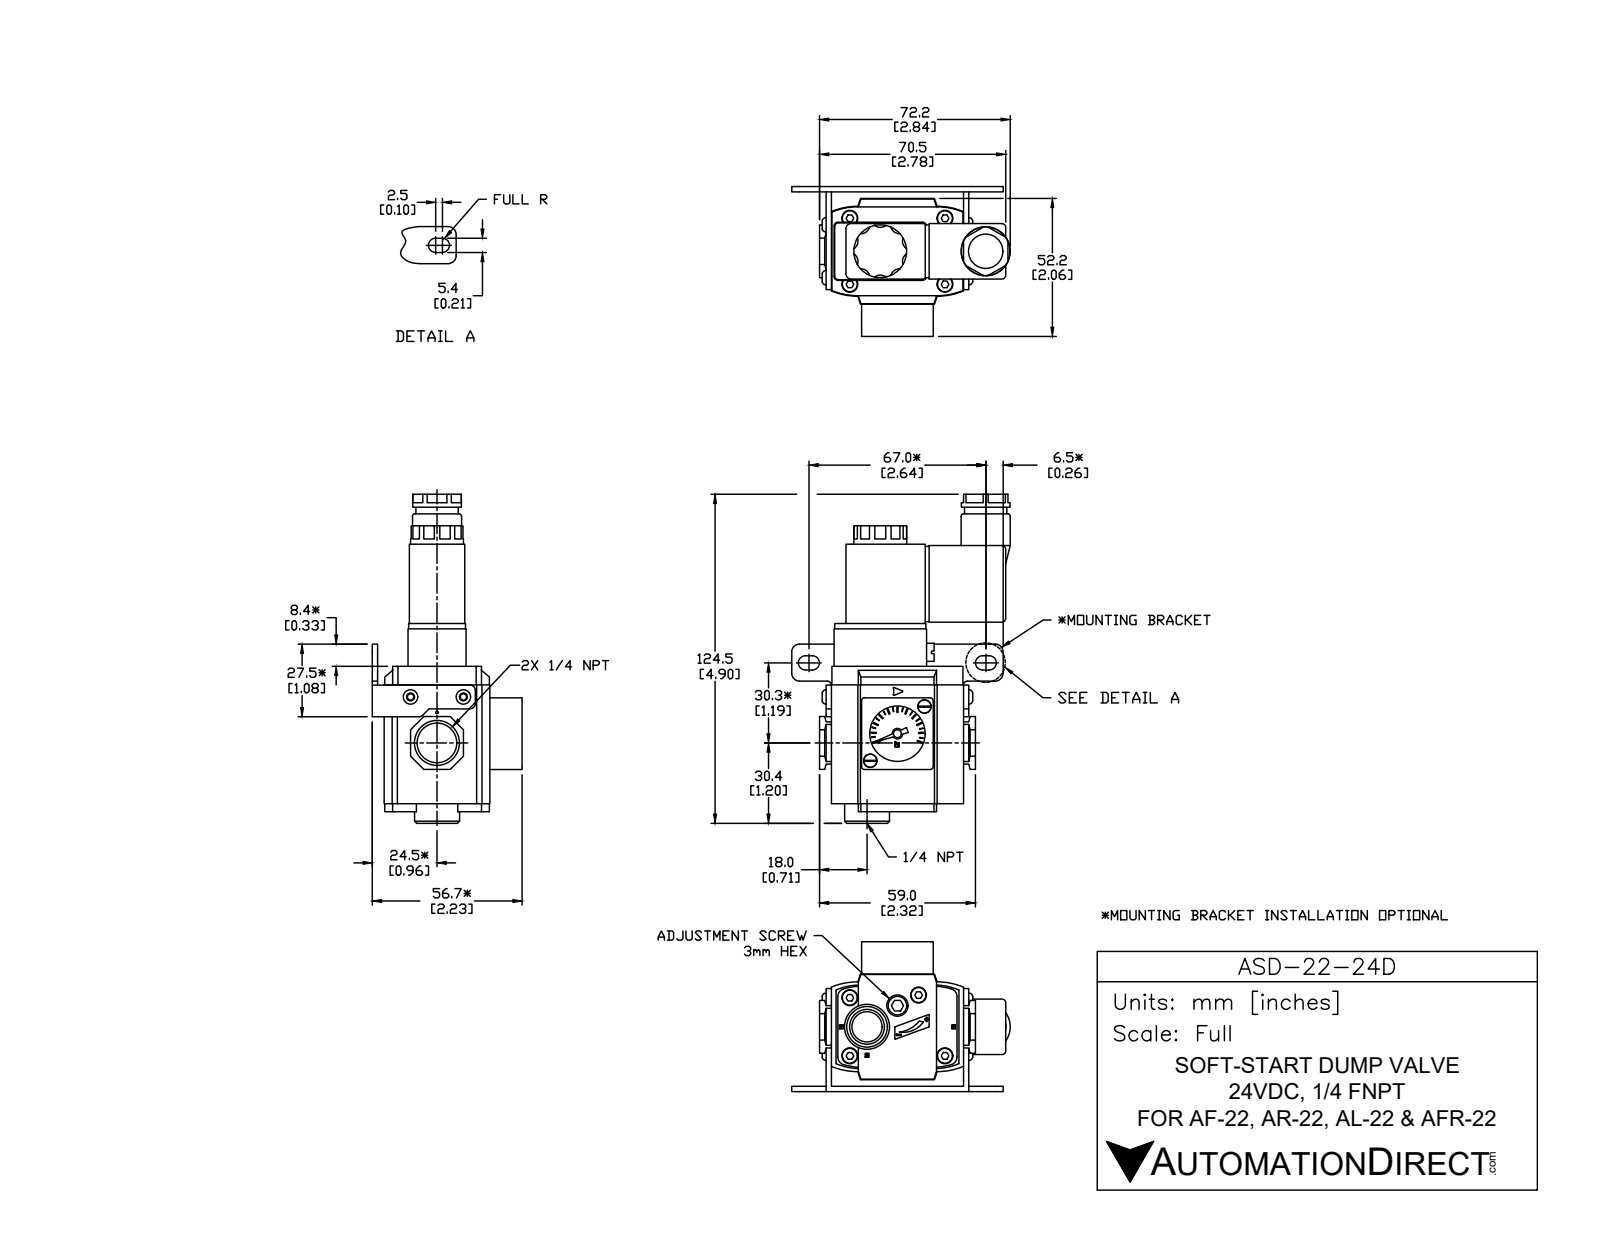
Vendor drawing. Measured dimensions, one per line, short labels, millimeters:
name: ASD-22-24D
written by: SolidWorks 2015 (CONFIG_CONTROL_DESIGN)
unit: mm
bodies: 22 solids, 568 faces (363 planar, 168 cylindrical, 37 other)
size: 124.5 × 82.7 × 56.7
volume: 163 664 mm³; area: 47 088 mm²
holes: 10× ⌀3, 8× ⌀6, 1× ⌀7, 1× ⌀8, 1× ⌀11.13, 1× ⌀11.45, 1× ⌀13, 1× ⌀17, 1× ⌀21
bosses: 4× ⌀5.6, 4× ⌀5.5, 2× ⌀2.5, 1× ⌀20, 1× ⌀18.6, 1× ⌀18.4, 1× ⌀16, 1× ⌀4
rounds: 10× R1.5, 10× R3.16, 6× R1, 6× R3, 4× R0.73, 4× R1.25, 4× R2.7, 4× R24.8
face distances: 52, 3, 2, 27.5, 6.5, 7, 45, 14, 5.5, 7.5
hole spacings: 1.5, 23.5, 36, 36.03, 42.99, 12.78, 14.09, 14.5
